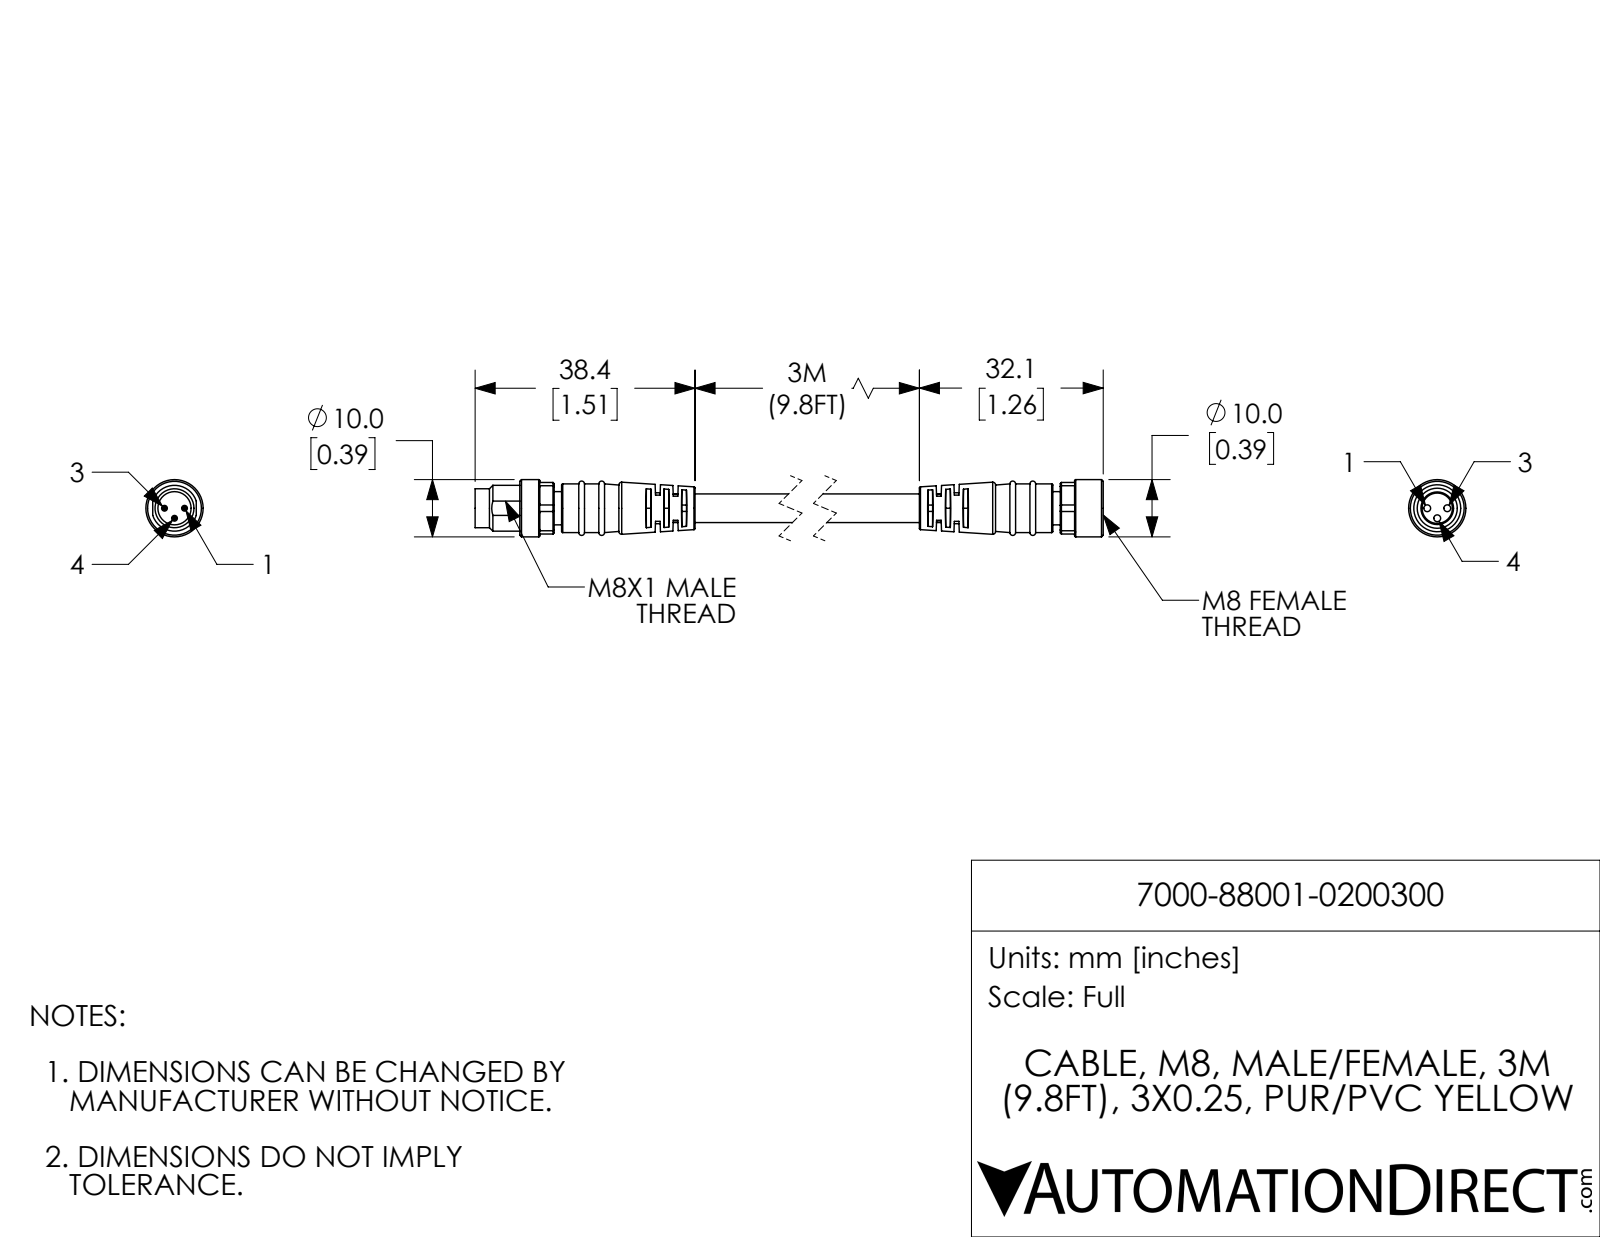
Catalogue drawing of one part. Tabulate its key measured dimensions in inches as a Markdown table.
| quantity | value |
| --- | --- |
| part name | 7000-88001-0200300; 7000-88001-0200300_FEMALE; 7000-88001-0200300_MALE |
| STEP written by | SolidWorks 2017 (AUTOMOTIVE_DESIGN) |
| units | inches |
| bodies | 2 solids, 273 faces (138 planar, 66 cylindrical, 69 other) |
| overall size | 4.823 × 0.394 × 0.394 |
| volume | 0.272 in³ |
| surface area | 5.608 in² |
| round holes (diameter × count) | 0.047 × 3, 0.276 × 1 |
| round bosses / shafts (diameter × count) | 0.039 × 3, 0.394 × 1, 0.335 × 1, 0.315 × 1, 0.268 × 1, 0.228 × 1, 0.224 × 1, 0.197 × 1 |
| partial cylindrical surfaces (radius × count) | 0.193 × 1 |
| main face-to-face distances | 0.122, 0.122, 0.025, 4.28, 0.147, 0.354, 0.051, 3.933, 0.026, 0.346 |
| hole center spacings | 0.069, 0.097, 0.138 |
